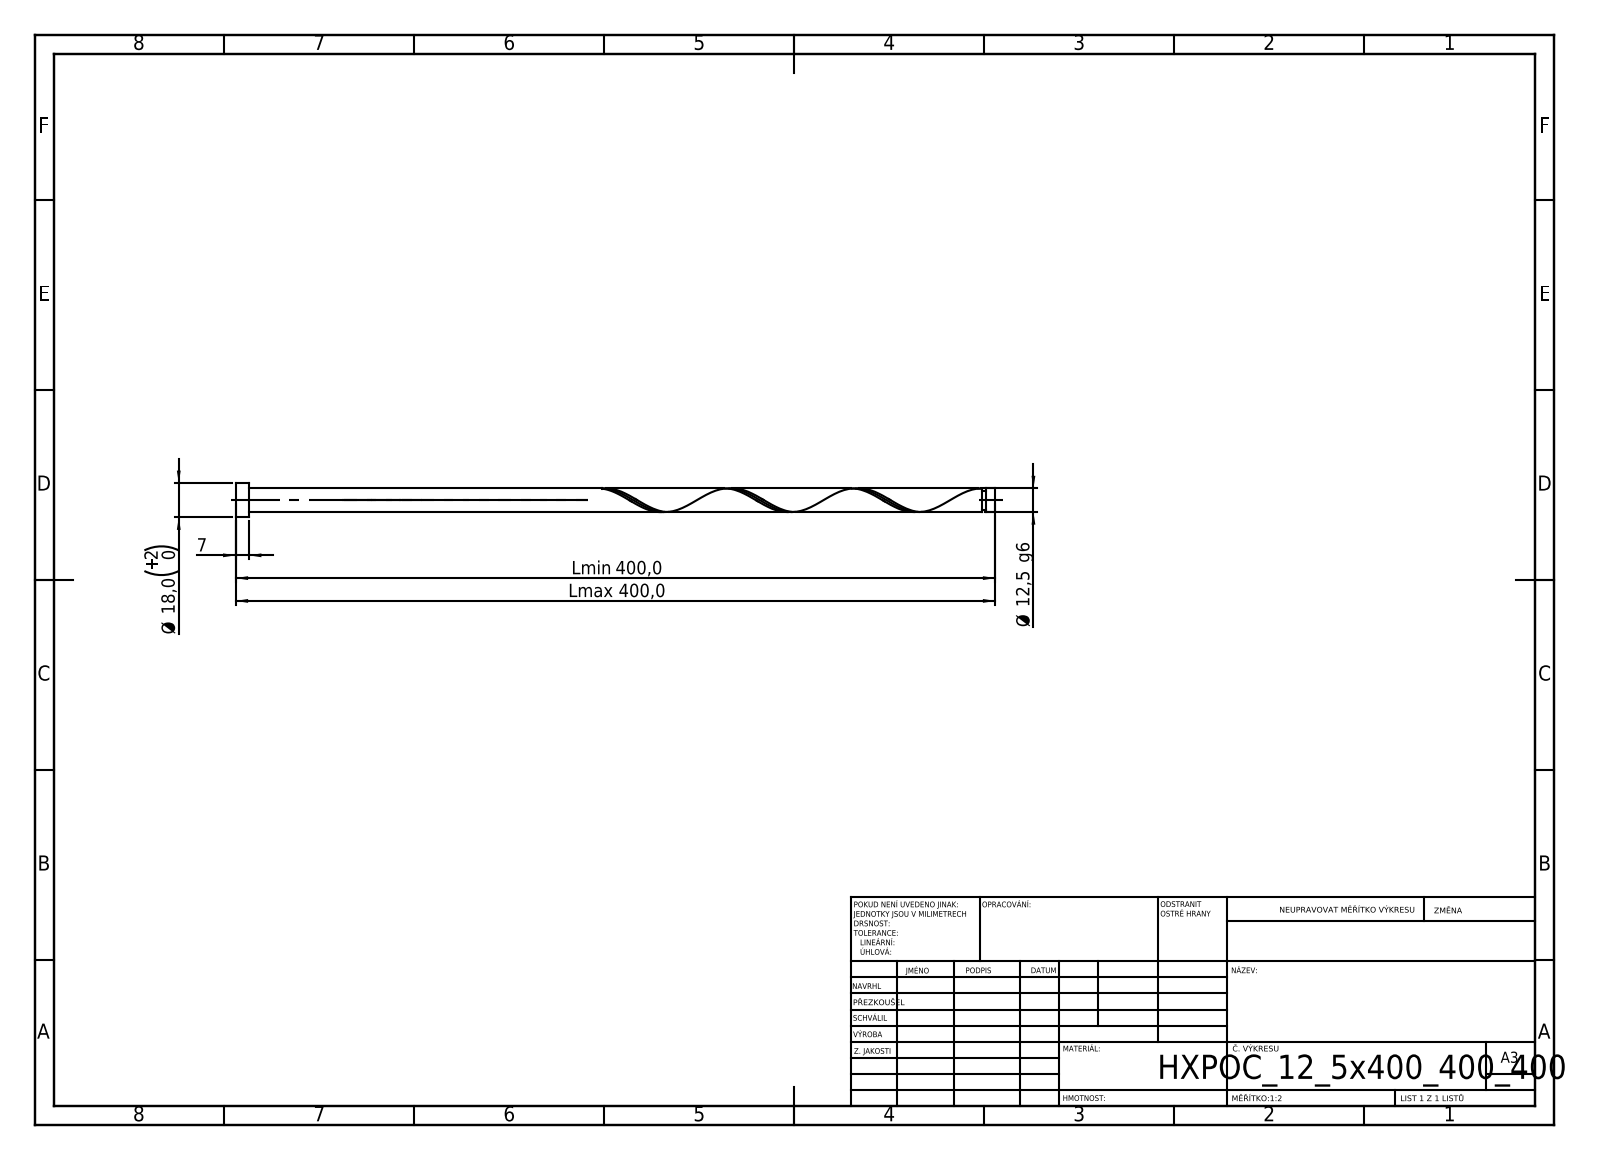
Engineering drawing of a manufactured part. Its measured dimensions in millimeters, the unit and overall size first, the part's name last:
Units: millimetres
Overall size (bounding box): 400 × 18 × 18
Round bosses / shafts (diameter × count): ⌀18 ×1, ⌀12.5 ×1, ⌀10 ×1
Main face-to-face distances: 7, 400, 393, 395.25, 388.25, 4.75, 392.75, 385.75, 2.5, 7.25
Volume: 49 429 mm³ · Surface area: 16 697 mm²
Bodies: 1 solid, 21 faces (6 planar, 14 cylindrical, 1 other)
STEP written by: SolidWorks 2019 (CONFIG_CONTROL_DESIGN)
